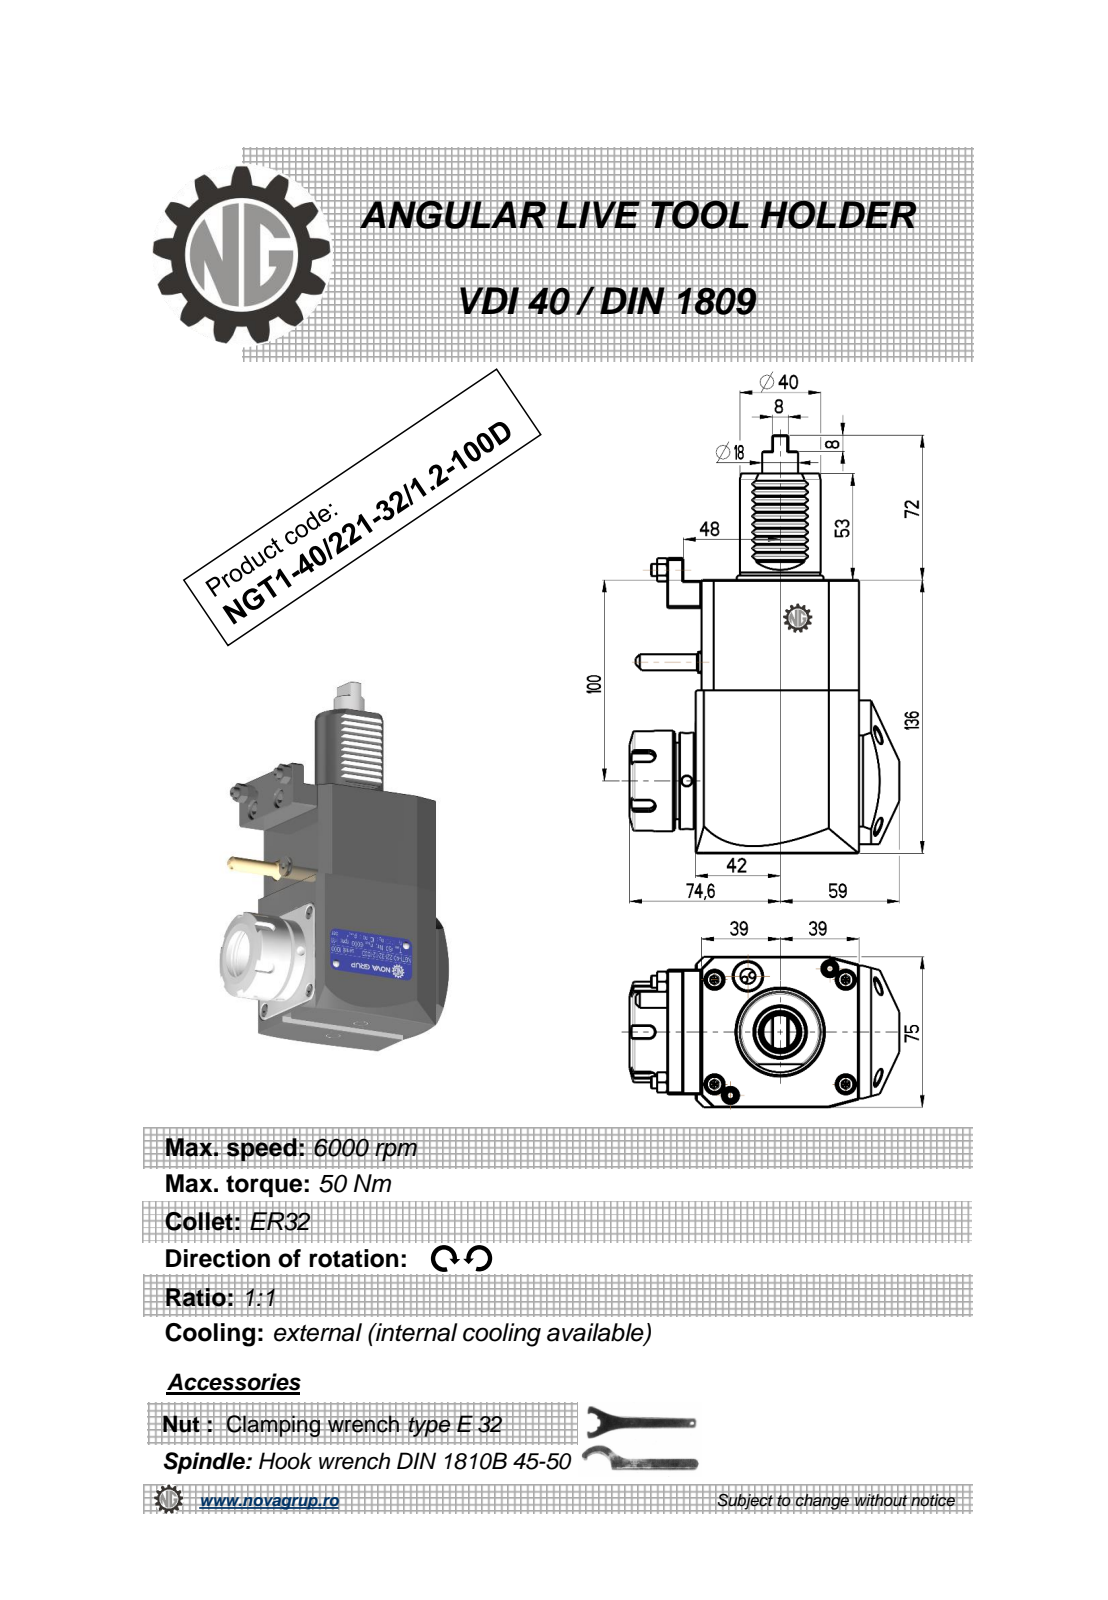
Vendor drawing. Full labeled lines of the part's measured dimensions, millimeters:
Part name (STEP PRODUCT): NGT1_40_221_32_1_2_100D
STEP written by: PRO/ENGINEER BY PARAMETRIC TECHNOLOGY CORPORATION, 2010280 (CONFIG_CONTROL_DESIGN)
Units: millimetres
Bodies: 1 solid, 383 faces (173 planar, 77 cylindrical, 133 other)
Overall size (bounding box): 208 × 133.6 × 76.6
Volume: 997 213 mm³ · Surface area: 76 673 mm²
Round holes (diameter × count): ⌀5 ×3, ⌀3 ×1, ⌀27 ×1
Round bosses / shafts (diameter × count): ⌀6 ×2, ⌀50 ×1, ⌀48 ×1, ⌀41 ×1, ⌀40 ×1, ⌀17.8 ×1, ⌀11.2 ×1, ⌀8 ×1
Partial cylindrical surfaces — rounded edges, fillets, slot ends (radius × count): R0.3 ×10, R0.31 ×10, R0.22 ×6, R3 ×5, R0.8 ×2, R0.5 ×1, R40 ×1
Main face-to-face distances: 75, 136, 78, 14, 81, 3, 2.8, 80.8, 0.5, 17
Hole centre spacings: 61.13
